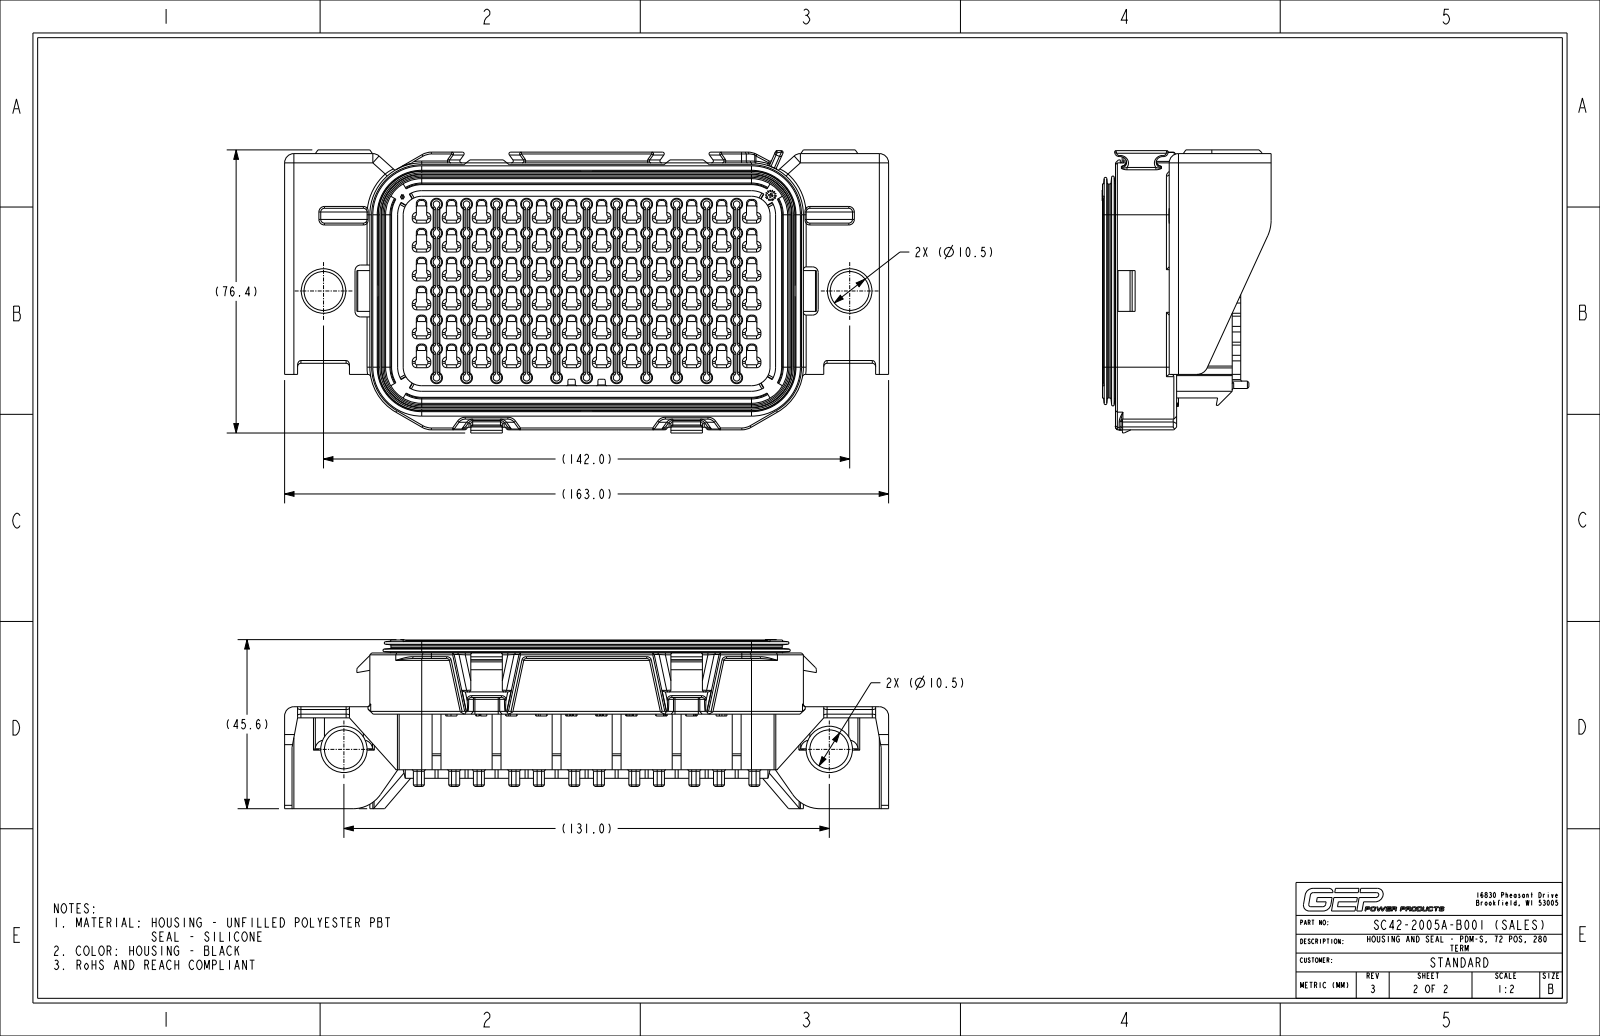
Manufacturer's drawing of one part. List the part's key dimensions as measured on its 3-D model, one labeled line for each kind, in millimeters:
Part name (STEP PRODUCT): PC26-2000A-B001_NCF; PC14-2000A-B002_INSTALLED_NCF; PC42-2005A-B001_SALES_NCF_ASM; SC42-2005A-B001_NCF_ASM
STEP written by: CREO PARAMETRIC BY PTC INC, 2024014 (CONFIG_CONTROL_DESIGN)
Units: millimetres
Bodies: 2 solids, 11879 faces (4043 planar, 3434 cylindrical, 4402 other)
Overall size (bounding box): 163 × 76.36 × 45.6
Volume: 126 941 mm³ · Surface area: 149 019 mm²
Round holes (diameter × count): ⌀6.7 ×72, ⌀10.5 ×4, ⌀12.5 ×2
Round bosses / shafts (diameter × count): ⌀4 ×1
Partial cylindrical surfaces — rounded edges, fillets, slot ends (radius × count): R0.5 ×729, R0.3 ×628, R0.4 ×350, R1 ×192, R0.8 ×146, R1.4 ×77, R4.45 ×72, R0.9 ×43
Main face-to-face distances: 2, 1.5, 5.5, 7.5, 9, 52.6, 54.1, 7, 9.5, 1.8
Hole centre spacings: 11.24, 7.8, 17.58, 15.6, 17.98, 25.52, 33.33, 8.1
